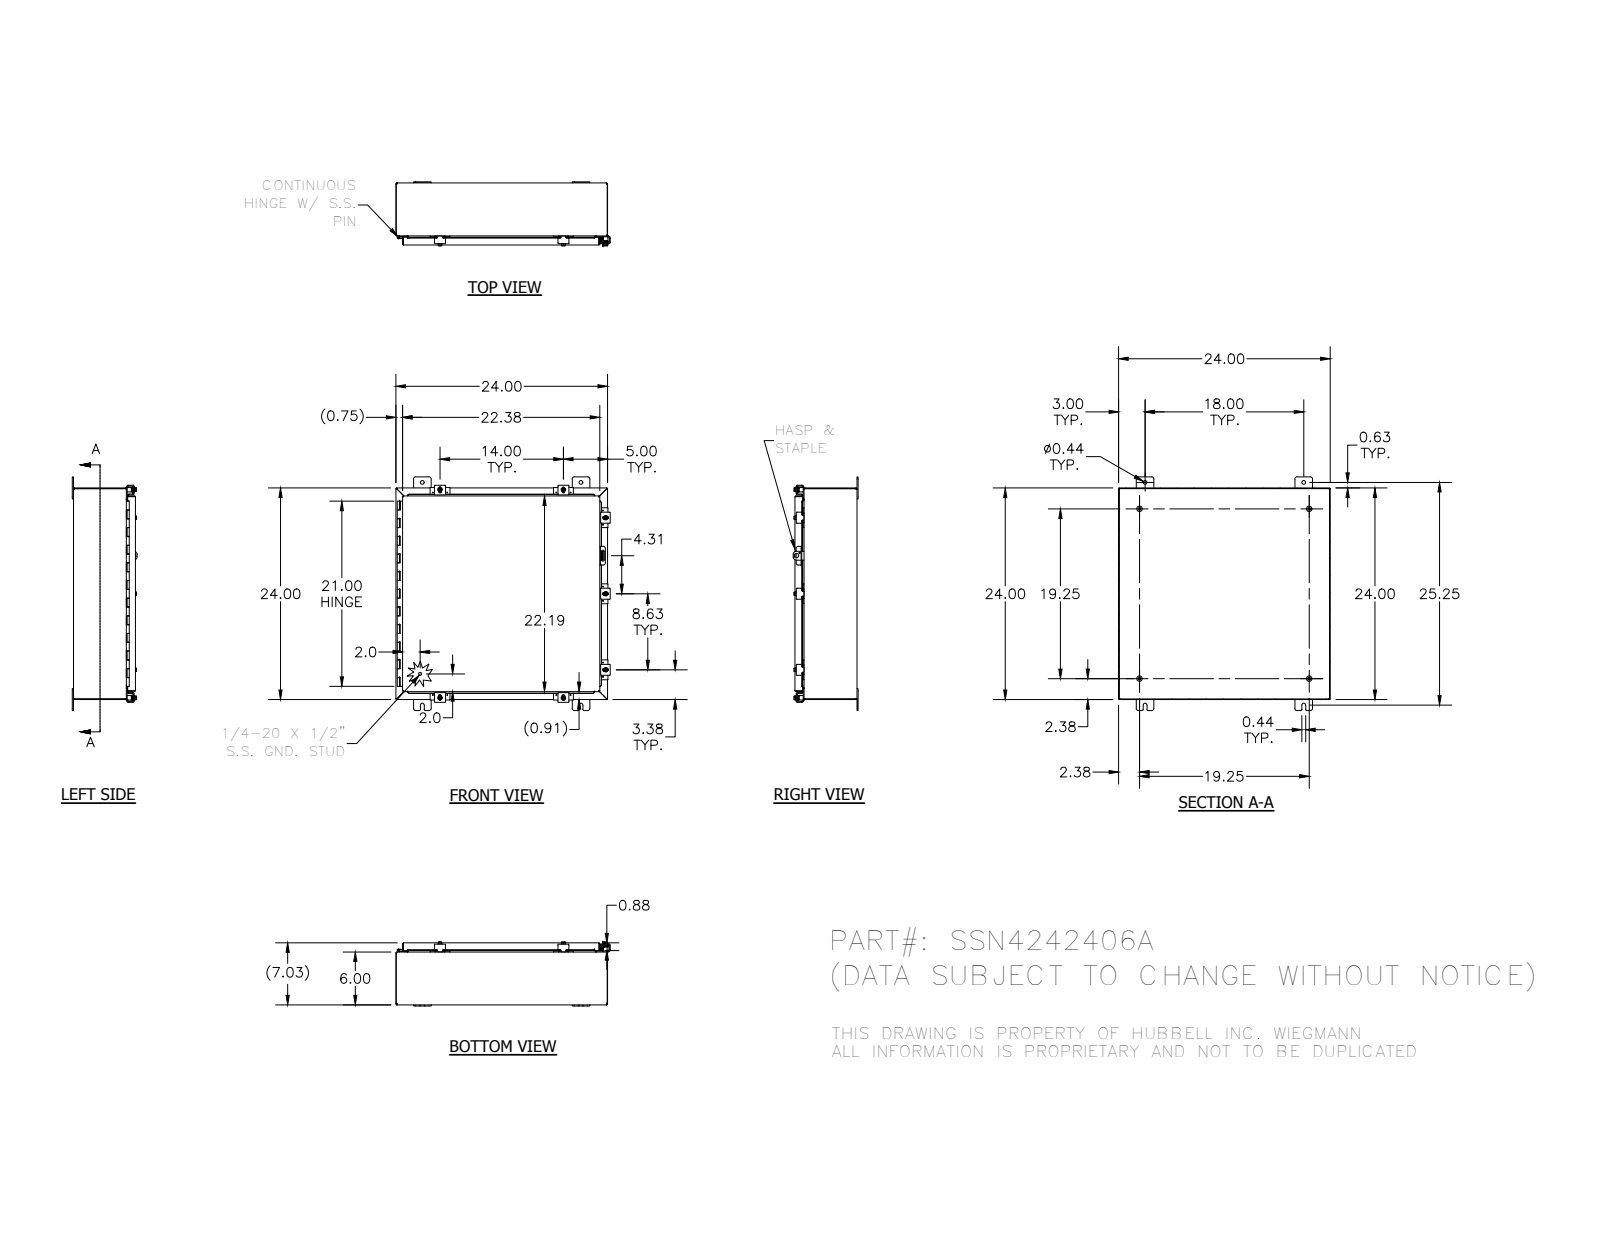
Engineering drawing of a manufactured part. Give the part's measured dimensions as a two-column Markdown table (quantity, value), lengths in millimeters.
| quantity | value |
| --- | --- |
| part name | 32912; 30818; SSN4242406ABKP; 30824-3 (+8 more) |
| STEP written by | SolidWorks 2014 (AUTOMOTIVE_DESIGN) |
| units | millimeters |
| bodies | 52 solids, 2024 faces (782 planar, 875 cylindrical, 367 other) |
| overall size | 673.1 × 615.1 × 186.8 |
| volume | 2 640 000 mm³ |
| surface area | 2 718 000 mm² |
| round holes (diameter × count) | 2.8 × 14, 5.4 × 7, 7.1 × 7, 7.6 × 7, 11.1 × 4, 3.2 × 1, 4 × 1, 12.7 × 1 |
| round bosses / shafts (diameter × count) | 6.4 × 9, 13.2 × 7, 12.7 × 7, 8.9 × 7, 15.9 × 4, 8.4 × 4, 8.6 × 1, 3 × 1 |
| partial cylindrical surfaces (radius × count) | 0.8 × 83, 3.2 × 37, 6.4 × 33, 0.8 × 23, 2.7 × 23, 1.6 × 18, 3.6 × 14, 2.5 × 10 |
| main face-to-face distances | 1.9, 176.8, 607.7, 174.9, 178.6, 609.6, 605.8, 150.5, 26.2, 152.4 |
| hole center spacings | 22.3, 591.9, 355.6, 41.3, 335.1, 376.3, 498.8, 583.2 |
